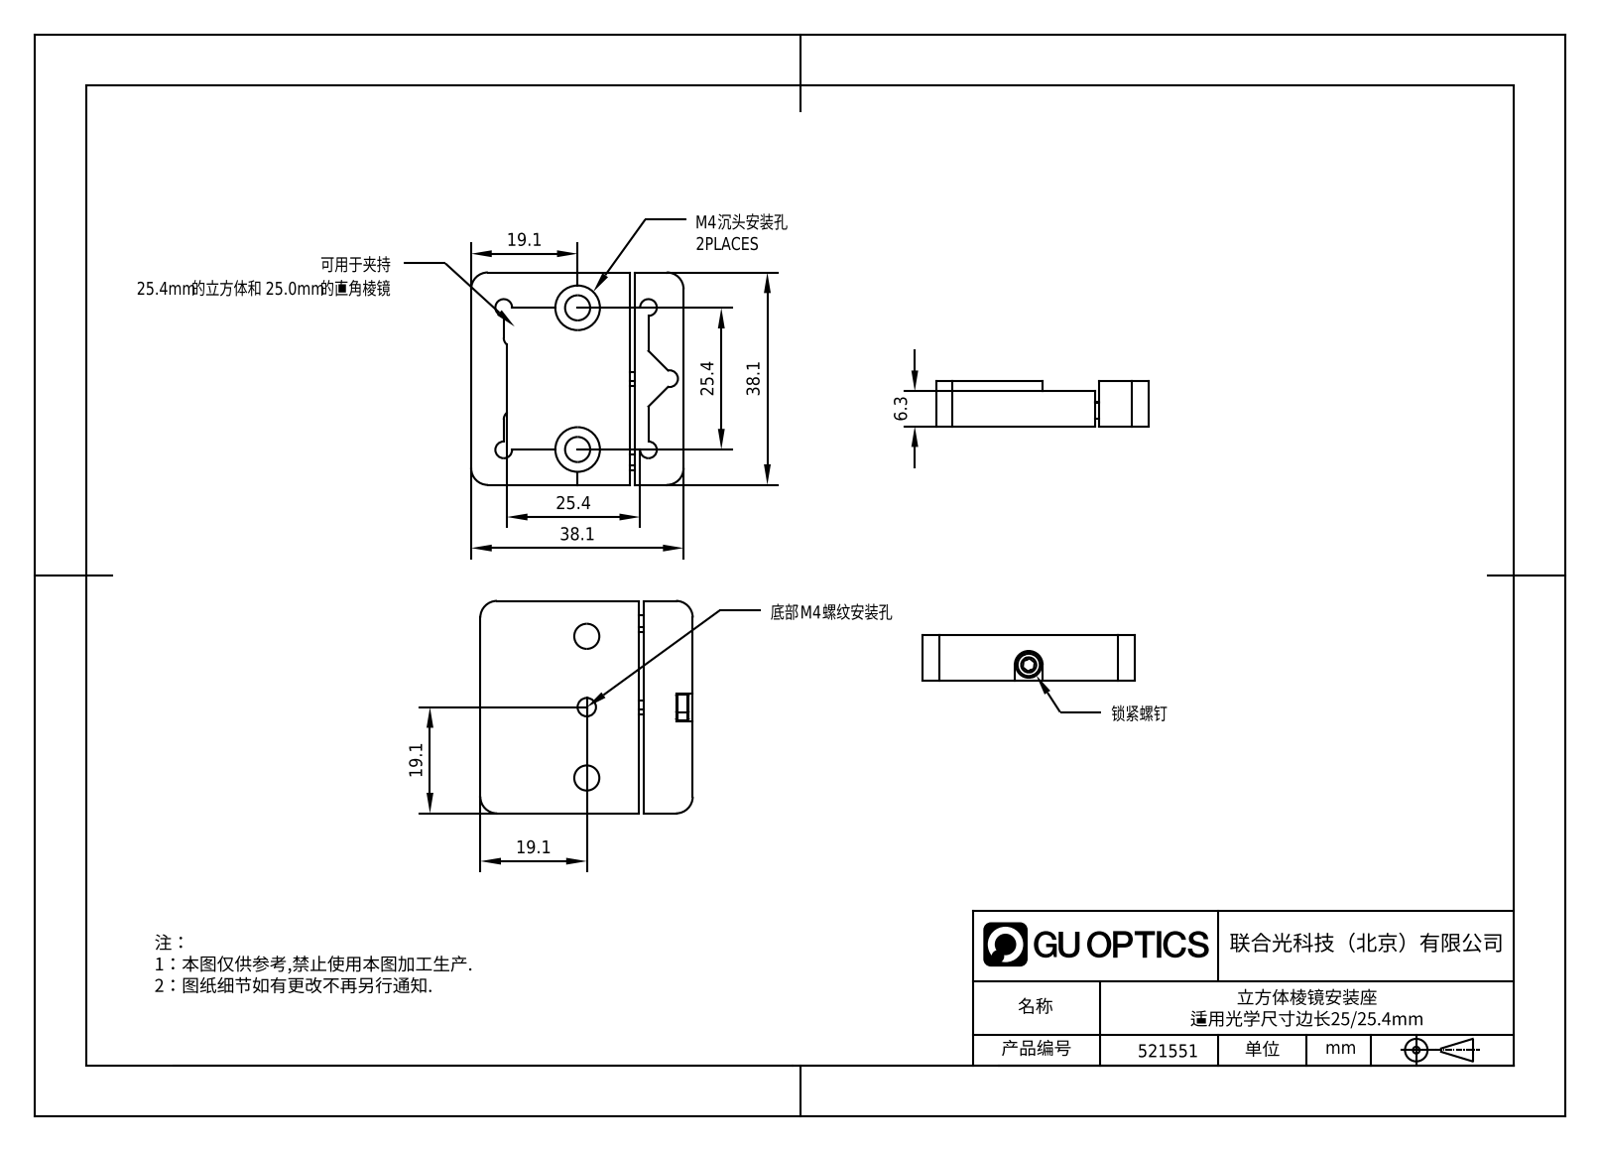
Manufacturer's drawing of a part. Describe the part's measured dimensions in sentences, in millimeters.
The part is named "1.3.13.2.2_平台安装座主体2，用于1英寸分束立方和直角棱镜，M4螺孔; 30.1.圆柱头内六角不锈钢螺丝_30.1.46-M2.5*10; 圆柱形磁铁_40.1.8-CY-4*3; 1.3.13.2.1_平台安装座主体1，用于1英寸分束立方和直角棱镜，M4螺孔 (+1 more)". Its 3-D file was written by "SolidWorks 2021 (CONFIG_CONTROL_DESIGN)". It is 5 solids with 168 faces: 78 planar, 54 cylindrical and 36 other. Overall it measures 38.1 by 38.1 by 8.2 millimeters. Its volume is 9 228 cubic millimeters and its surface area 5 666 square millimeters. Round holes: 2 of diameter 3, 2 of diameter 4, 2 of diameter 4.5, 2 of diameter 8, 1 of diameter 2.05, 1 of diameter 2.9, 1 of diameter 3.3. Round bosses or shafts: 1 of diameter 4.6, 1 of diameter 2.5. Partial cylindrical surfaces (rounded edges, fillets, slot ends): 5 of radius 1.5, 4 of radius 3, 2 of radius 1.59, 1 of radius 2.5. The main face-to-face distances are 6.3, 8.2, 1.9, 38.1, 28.5, 8.8, 29.3, 0.8, 9.6, 6. The hole center spacings are 7, 8, 12.7, 15, 23, 16, 25.4, 30.
